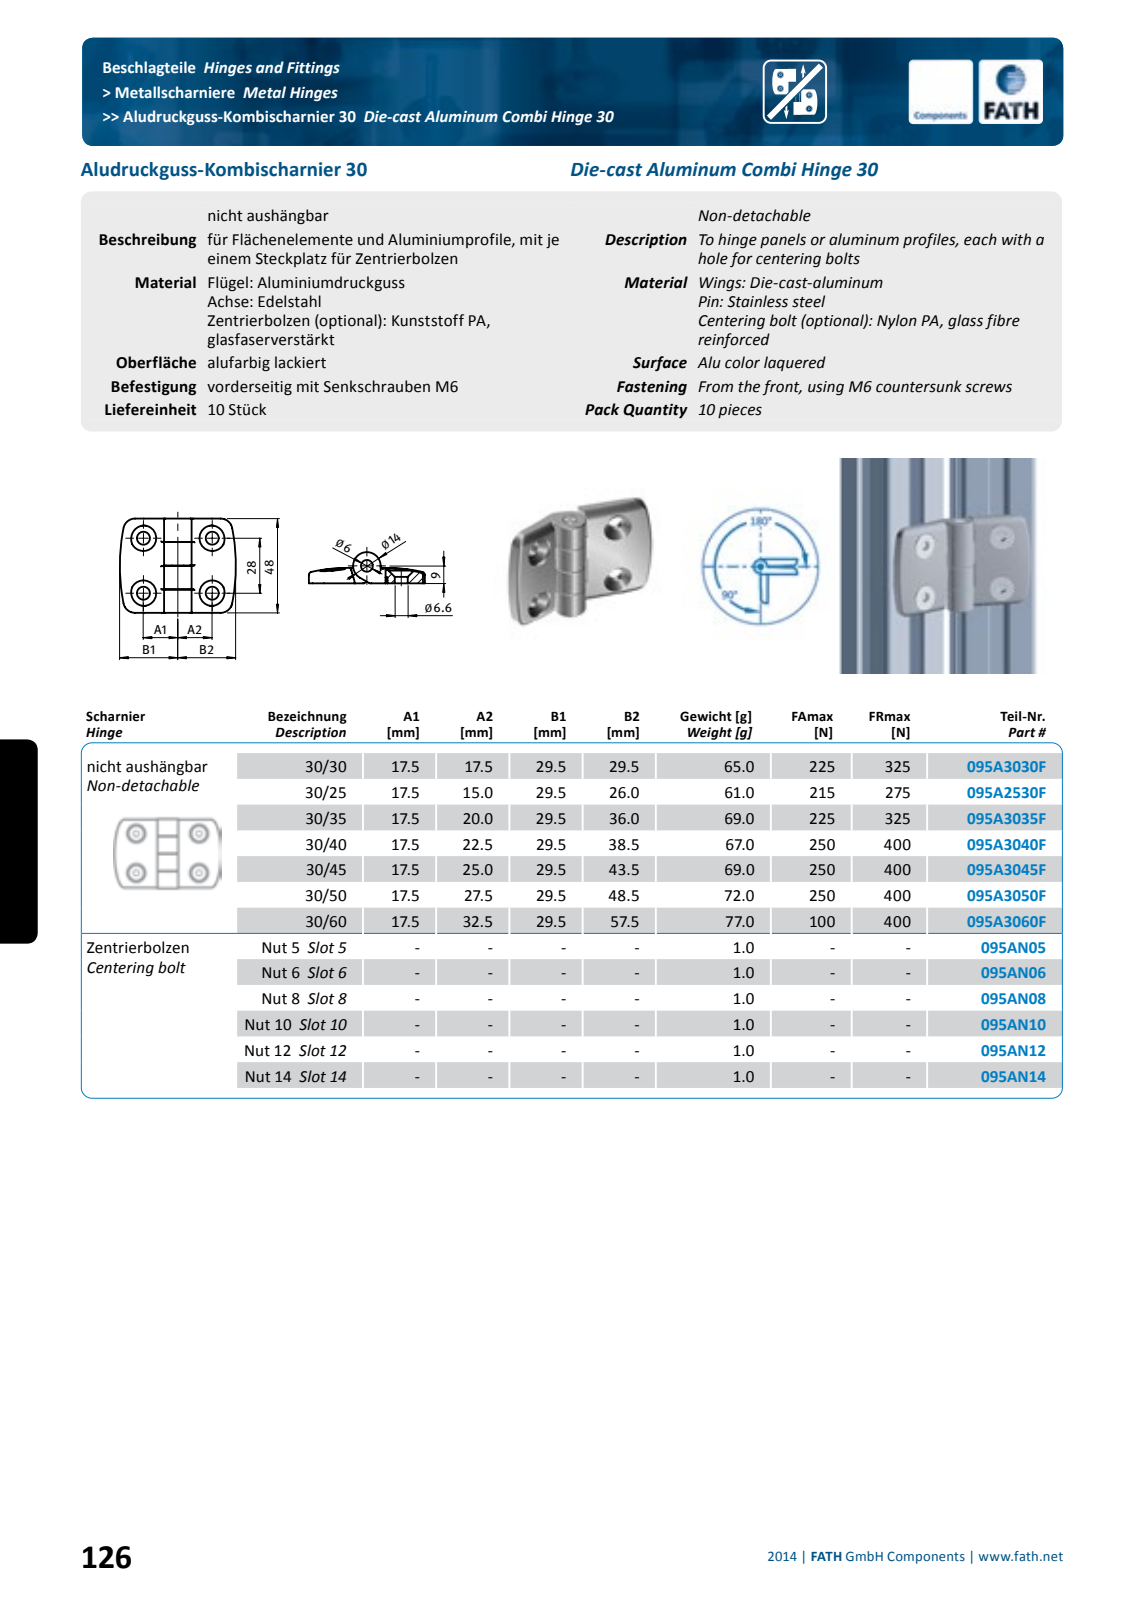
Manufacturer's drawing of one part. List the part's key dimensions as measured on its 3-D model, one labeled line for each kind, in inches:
Part name (STEP PRODUCT): fath_095a3030f_1; fath_095a3030f_2; fath_095a3030f_3; fath_095a3030f_4 (+1 more)
STEP written by: Spatial InterOp 3D (automotive_design)
Units: inches
Bodies: 5 solids, 672 faces (248 planar, 188 cylindrical, 236 other)
Overall size (bounding box): 2.323 × 1.89 × 0.719
Volume: 1.288 in³ · Surface area: 19.76 in²
Round holes (diameter × count): ⌀0.512 ×4, ⌀0.236 ×1
Round bosses / shafts (diameter × count): ⌀0.551 ×1
Partial cylindrical surfaces — rounded edges, fillets, slot ends (radius × count): R0.02 ×54, R0.008 ×20, R0.012 ×16, R0.236 ×4, R0.157 ×2, R3.937 ×2, R0.122 ×1
Main face-to-face distances: 0.118, 0.469, 1.421, 0.472, 0.48, 0.11, 0.941, 0.949, 0.953, 1.89
Hole centre spacings: 1.102, 1.378, 1.765
